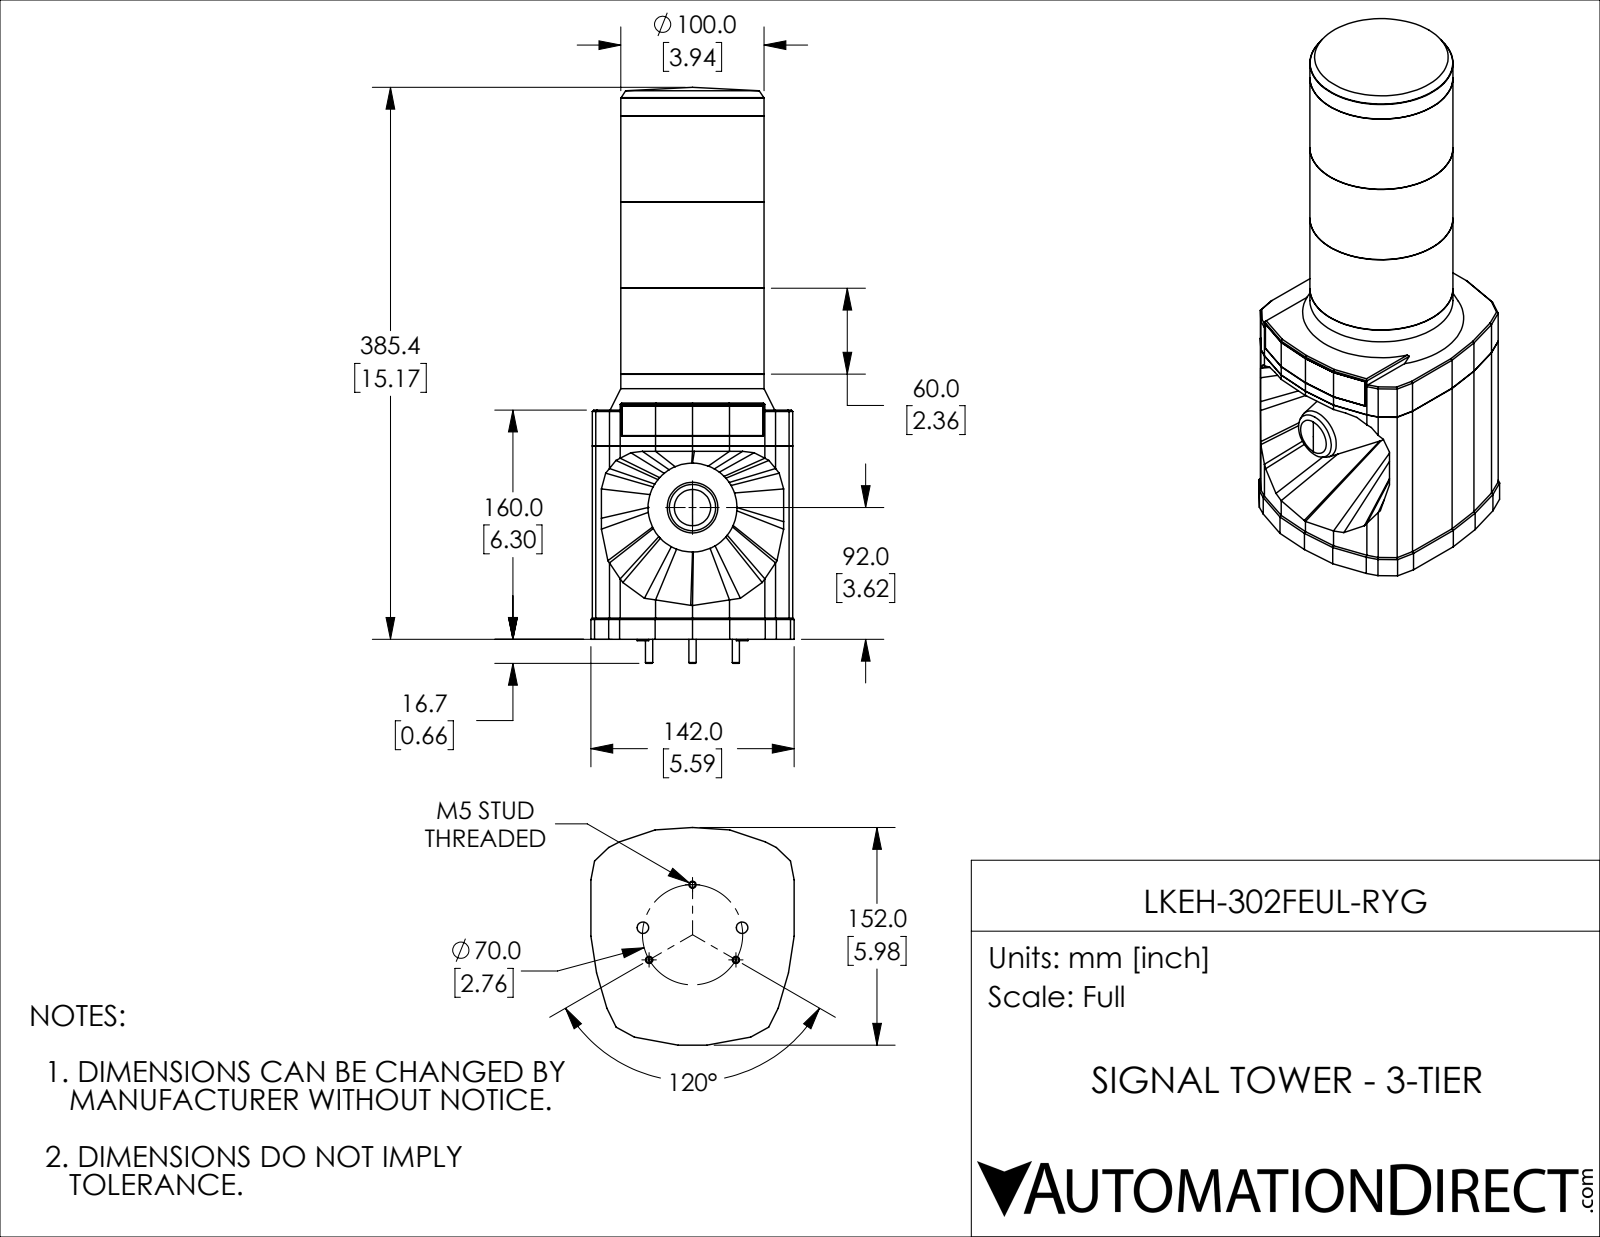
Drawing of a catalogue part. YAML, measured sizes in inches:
part_name: "LKEH-302FEUL-RYG"
step_written_by: "SolidWorks 2018 (AUTOMOTIVE_DESIGN)"
units: inches
bodies: {solids: 1, faces: 274, planar: 184, cylindrical: 28, other: 62}
overall_size: [15.831, 5.984, 5.591]
volume: 260.6
surface_area: 335.2
round_bosses_or_shafts:
  - {diameter: 0.197, count: 3}
  - {diameter: 0.315, count: 2}
  - {diameter: 3.937, count: 1}
  - {diameter: 3.764, count: 1}
face_to_face_distances: [0.039, 5.512, 6.299, 2.366, 6.496, 0.197, 2.362, 2.37, 4.732, 4.728]
